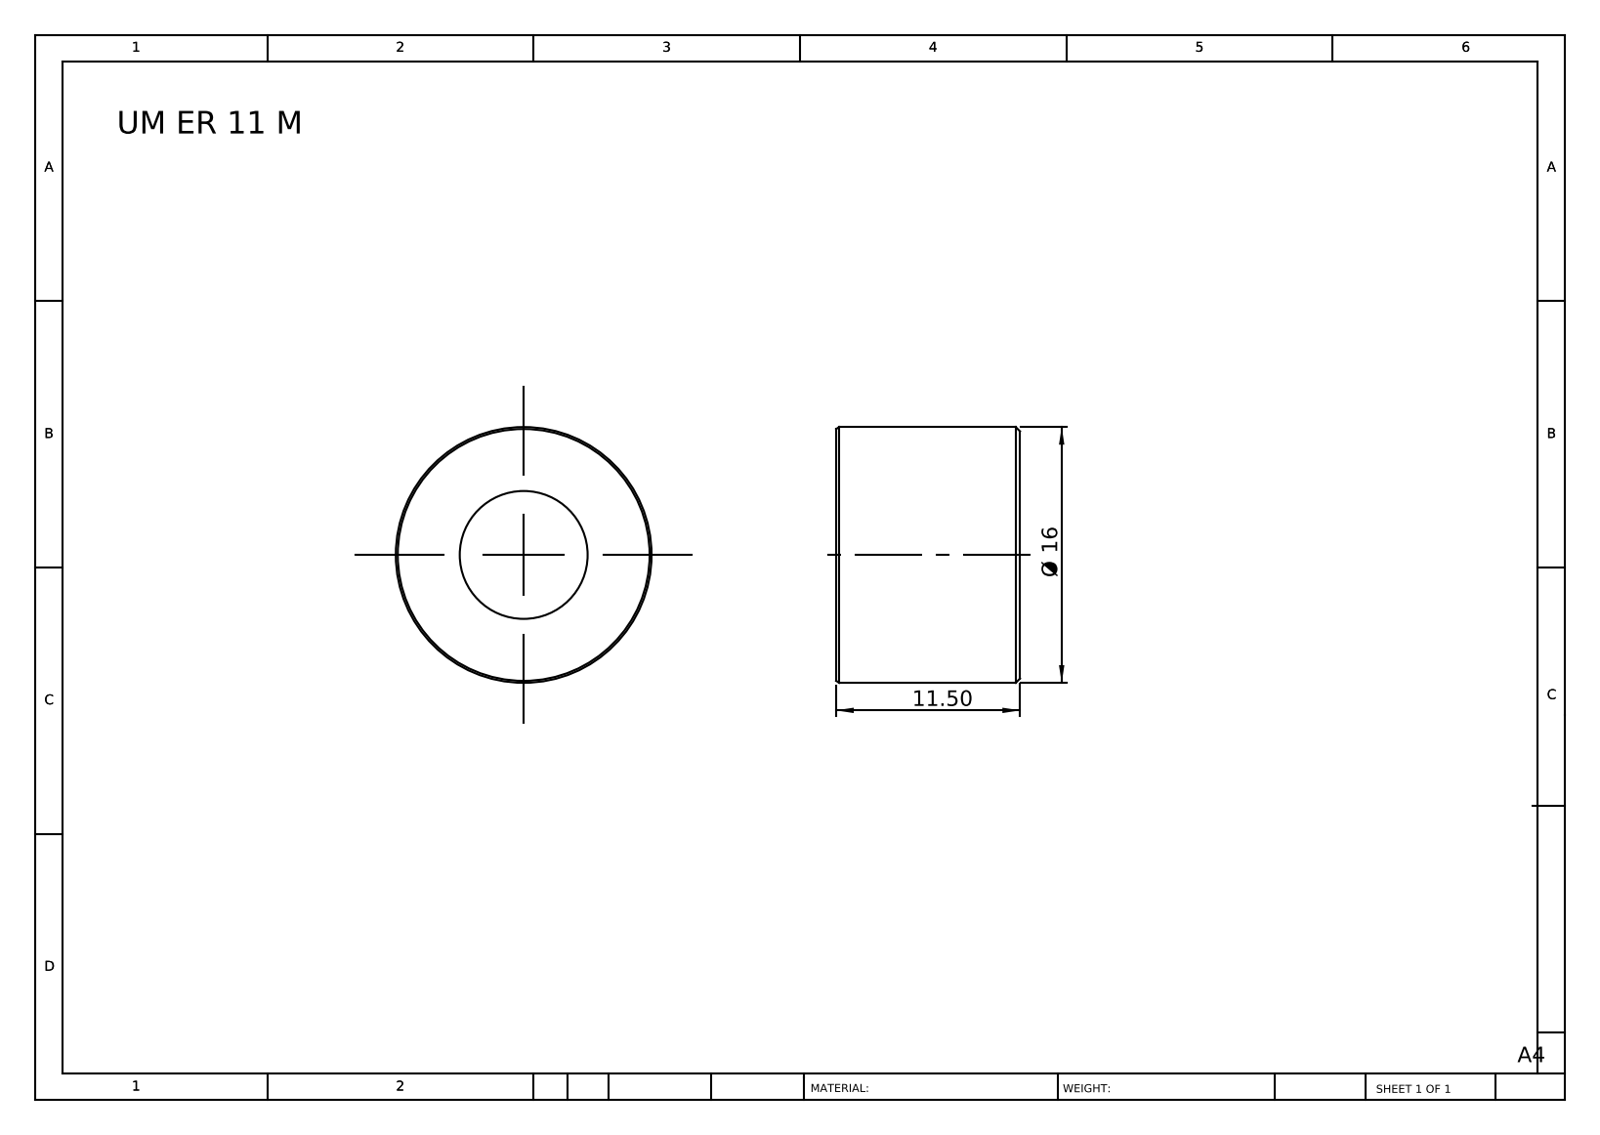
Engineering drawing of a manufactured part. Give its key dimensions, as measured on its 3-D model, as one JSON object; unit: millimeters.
{"part_name": "UM ER 11 M", "step_written_by": "SolidWorks 2014 (CONFIG_CONTROL_DESIGN)", "units": "millimeters", "bodies": {"solids": 1, "faces": 10, "planar": 2, "cylindrical": 4, "other": 4}, "overall_size": [16, 16, 11.5], "volume_mm3": 1732, "surface_area_mm2": 1156, "round_holes": [[8, 1]], "round_bosses_or_shafts": [[16, 1]], "face_to_face_distances": [11.5]}
